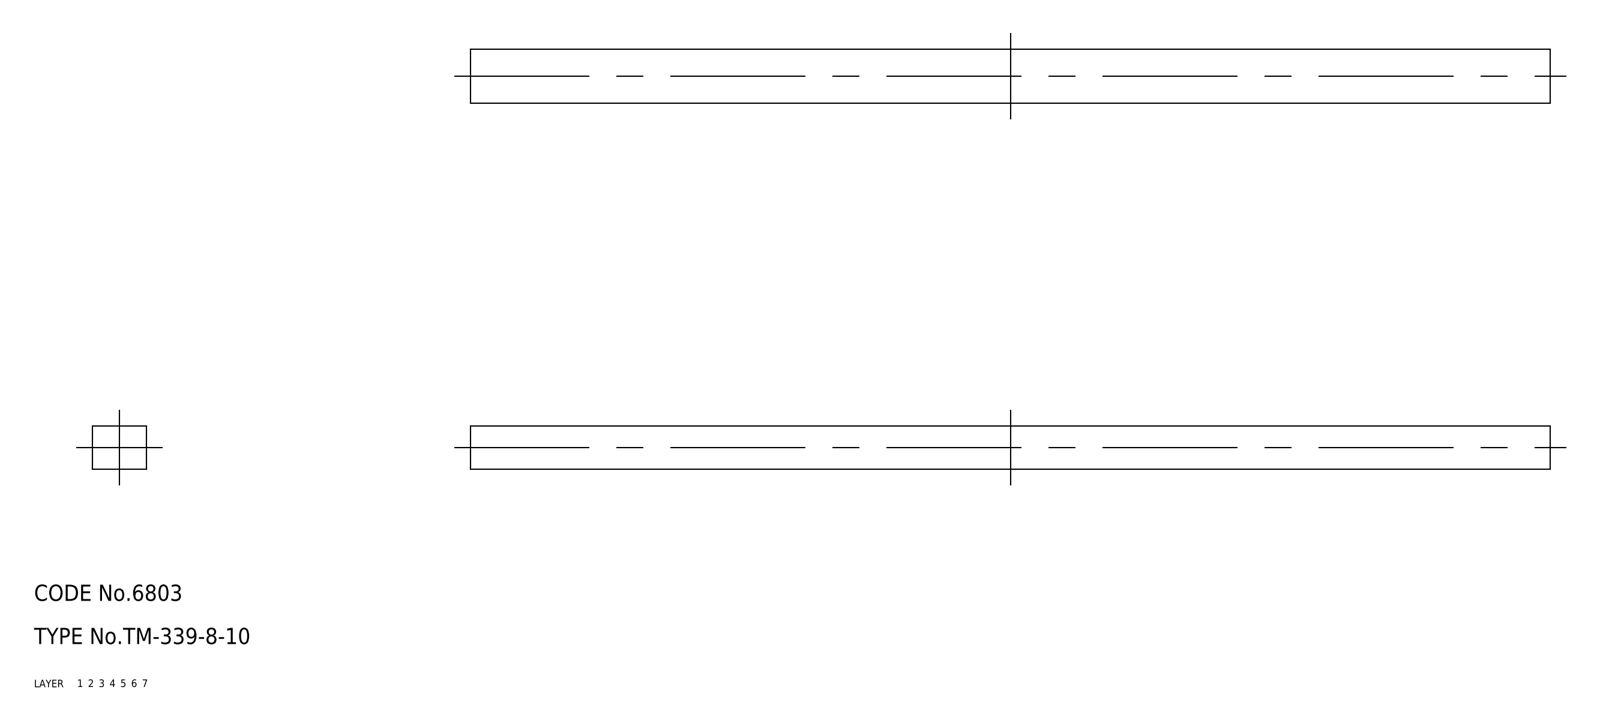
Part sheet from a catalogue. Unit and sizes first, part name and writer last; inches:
Units: inches
Overall size (bounding box): 7.874 × 0.394 × 0.315
Main face-to-face distances: 0.315, 0.394, 7.874
Volume: 0.976 in³ · Surface area: 11.41 in²
Bodies: 1 solid, 6 faces (6 planar, 0 cylindrical, 0 other)
Part name (STEP PRODUCT): rubber foam; TM_339_8_10
STEP written by: SolidWorks 2015 (AUTOMOTIVE_DESIGN)
